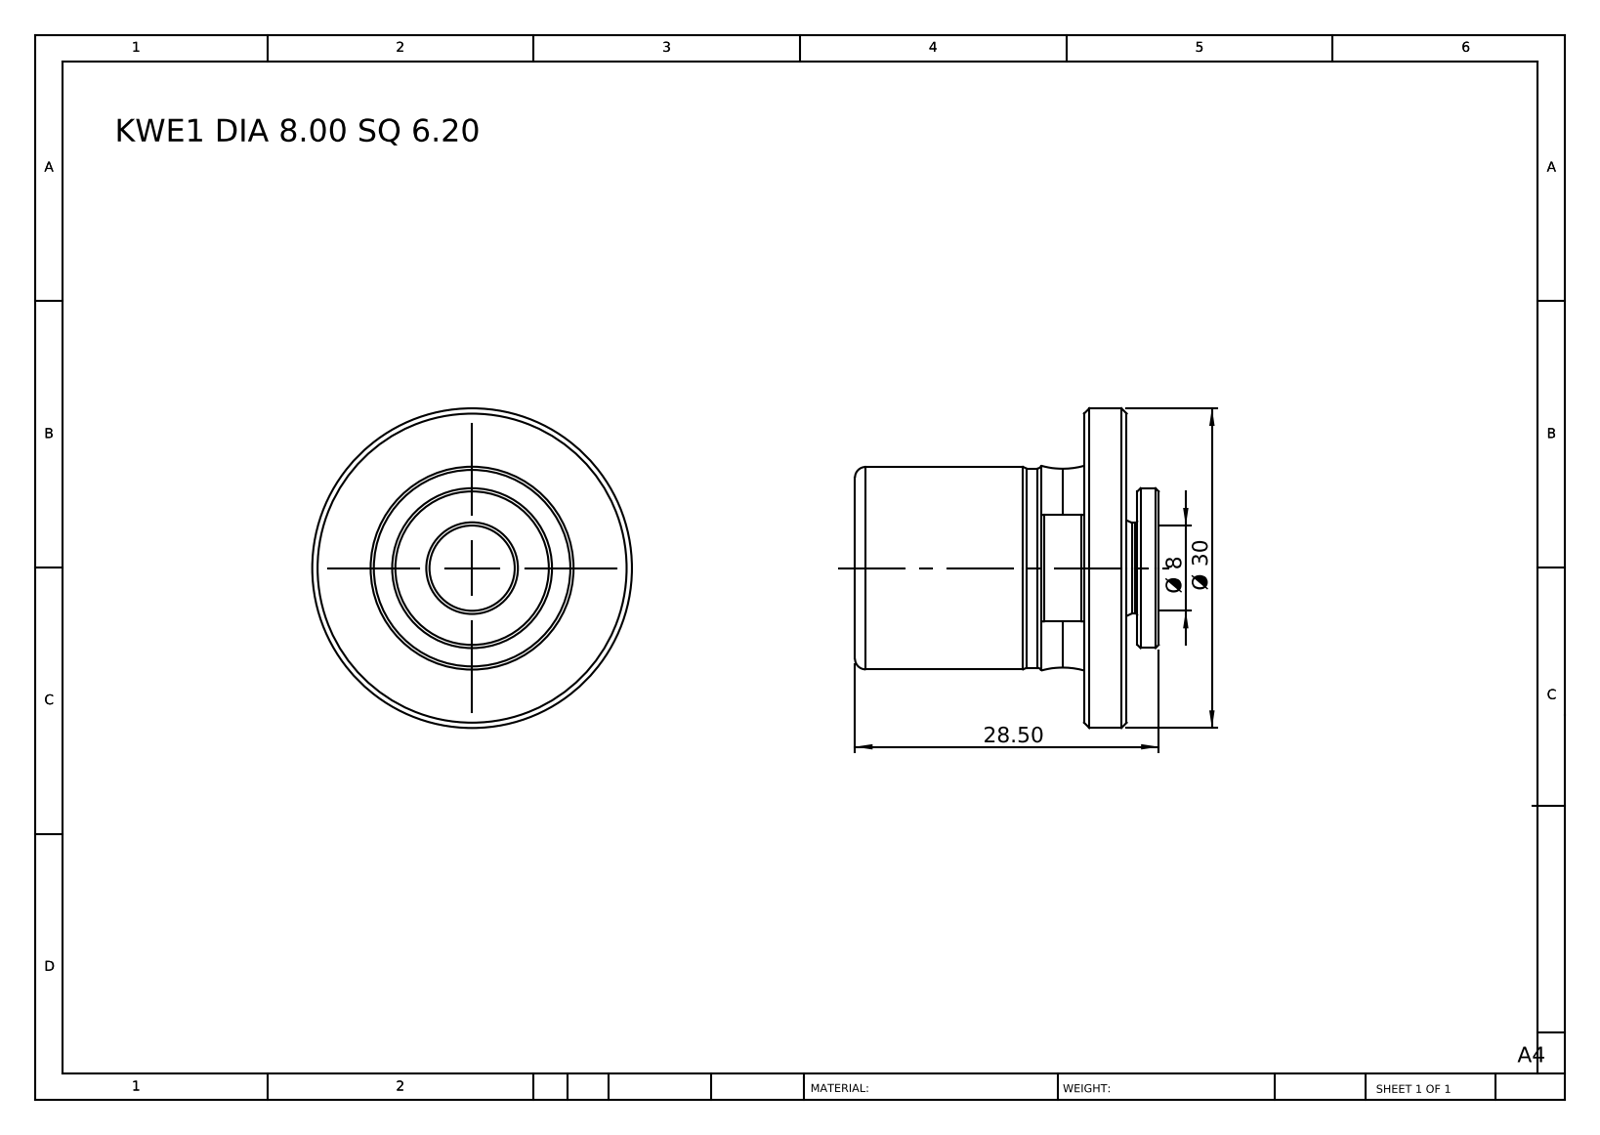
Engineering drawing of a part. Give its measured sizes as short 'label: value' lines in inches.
name: KWE1 DIA 8.00 SQ 6.20
written by: SolidWorks 2014 (CONFIG_CONTROL_DESIGN)
unit: in
bodies: 1 solid, 61 faces (13 planar, 16 cylindrical, 32 other)
size: 1.181 × 1.181 × 1.122
volume: 0.534 in³; area: 5.865 in²
holes: 1× ⌀0.315, 1× ⌀0.75
bosses: 1× ⌀1.181, 1× ⌀0.748, 1× ⌀0.736, 1× ⌀0.591, 1× ⌀0.335
rounds: 1× R0.488
face distances: 0.157, 0.846, 1.004, 1.122, 0.276, 0.118, 1.043, 0.197, 0.039, 0.079
